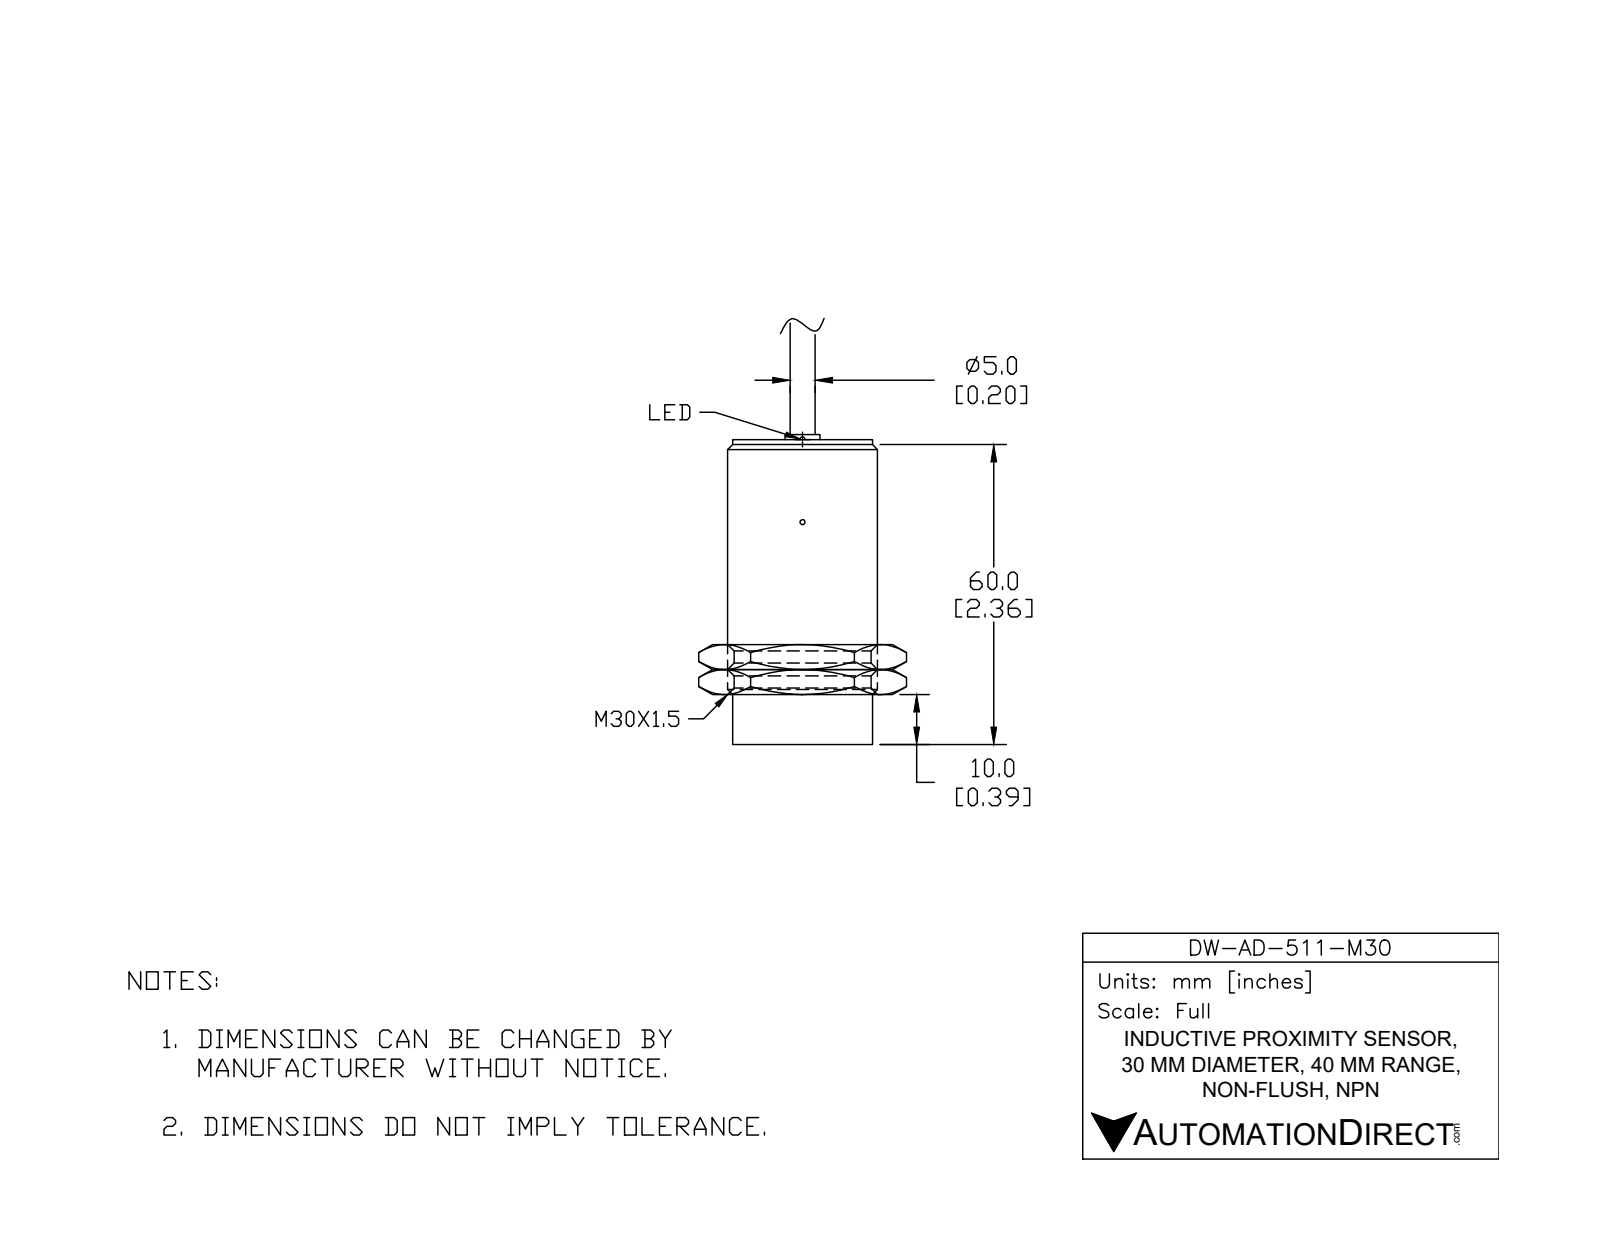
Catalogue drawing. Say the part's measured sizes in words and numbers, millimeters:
The part is named "DW-AD-511-M30". Its 3-D file was written by "SolidWorks 2017 (AUTOMOTIVE_DESIGN)". It is 2 solids with 16 faces: 6 planar, 4 cylindrical and 6 other. Overall it measures 88 by 30 by 30 millimeters. Its volume is 42 520 cubic millimeters and its surface area 8 600 square millimeters. Round bosses or shafts: 1 of diameter 30, 1 of diameter 27.5, 1 of diameter 10.5, 1 of diameter 5. The main face-to-face distances are 10, 61, 51, 61.7, 51.8, 0.8, 88, 78, 27, 26.2.
